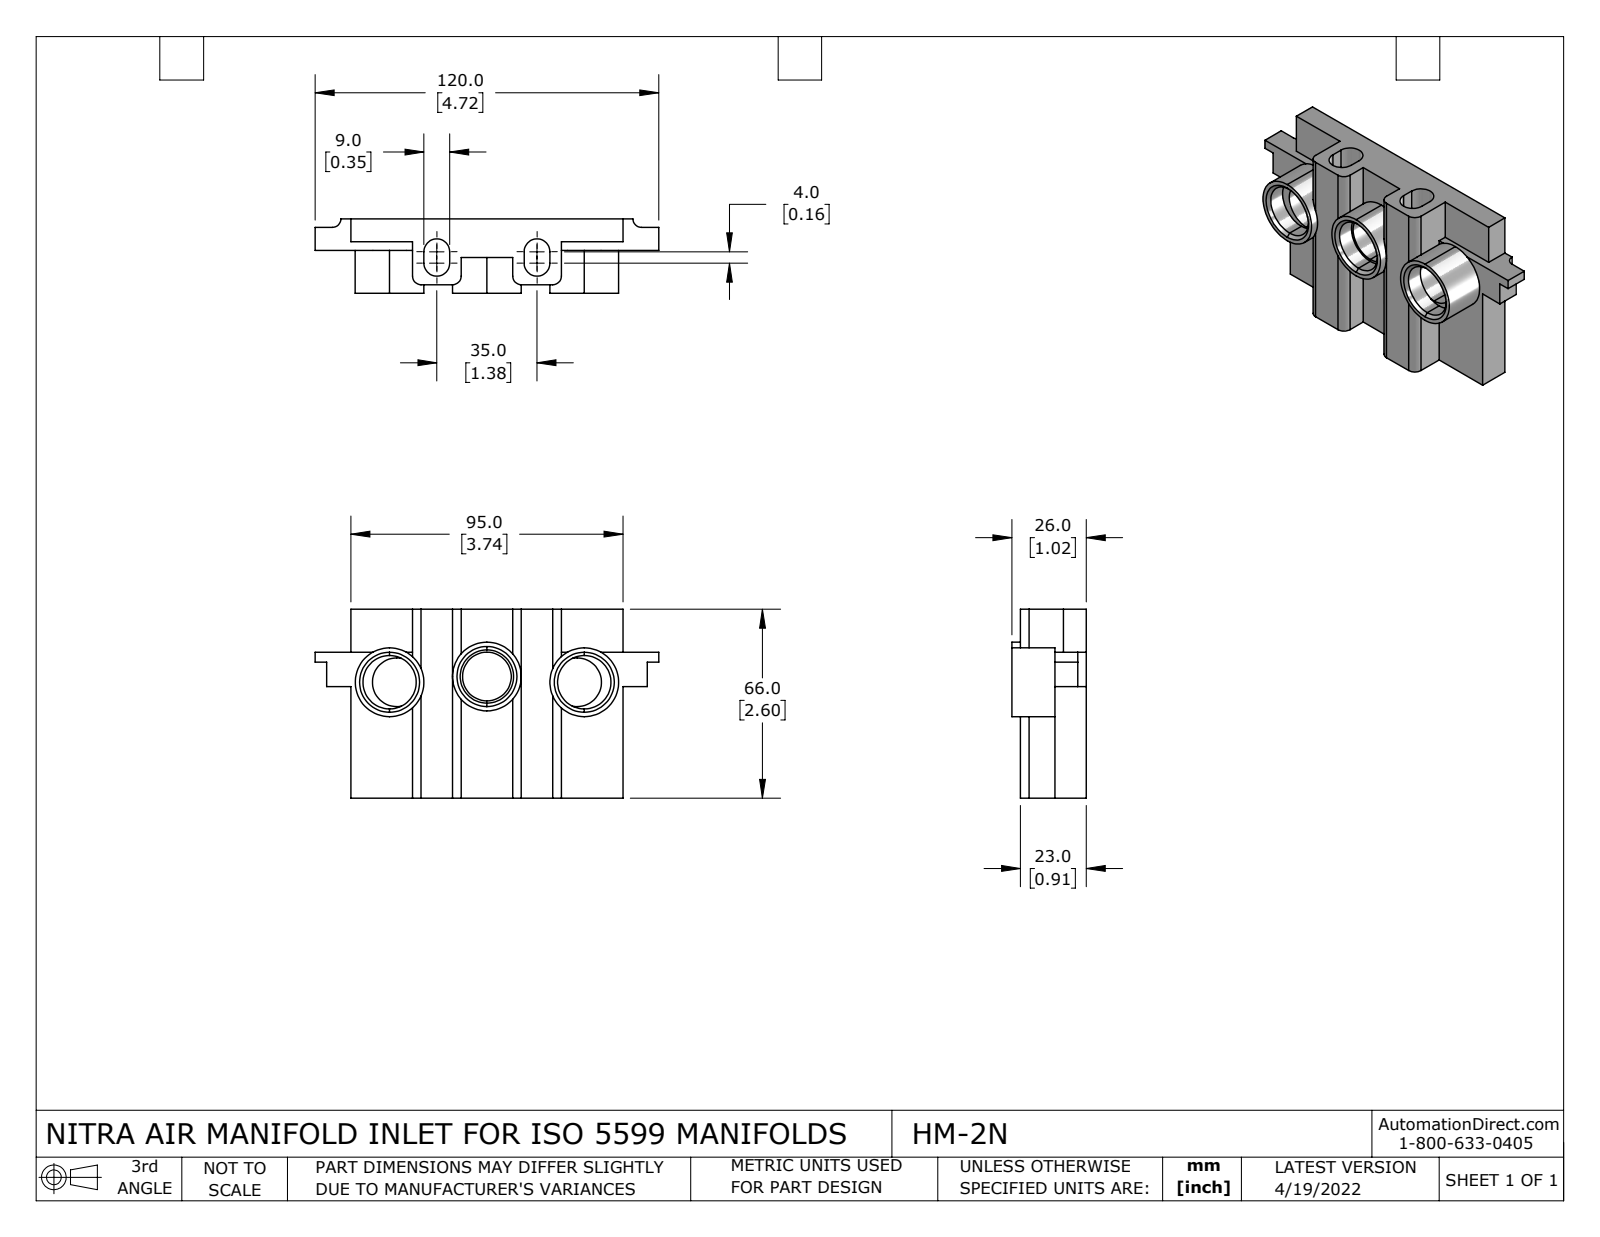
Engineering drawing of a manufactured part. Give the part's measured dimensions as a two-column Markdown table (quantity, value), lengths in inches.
| quantity | value |
| --- | --- |
| part name | HM-2N |
| STEP written by | SolidWorks 2021 (CONFIG_CONTROL_DESIGN) |
| units | inches |
| bodies | 1 solid, 98 faces (54 planar, 38 cylindrical, 6 other) |
| overall size | 4.724 × 2.598 × 1.024 |
| volume | 5.071 in³ |
| surface area | 45.84 in² |
| round holes (diameter × count) | 0.669 × 3, 0.733 × 3, 0.827 × 3 |
| round bosses / shafts (diameter × count) | 0.945 × 3 |
| partial cylindrical surfaces (radius × count) | 0.118 × 6, 0.177 × 4 |
| main face-to-face distances | 0.433, 0.906, 0.472, 0.118, 0.157, 0.591, 0.315, 1.378, 2.598, 0.512 |
| hole center spacings | 0.098, 1.243, 1.341, 2.579, 2.48, 2.677 |
